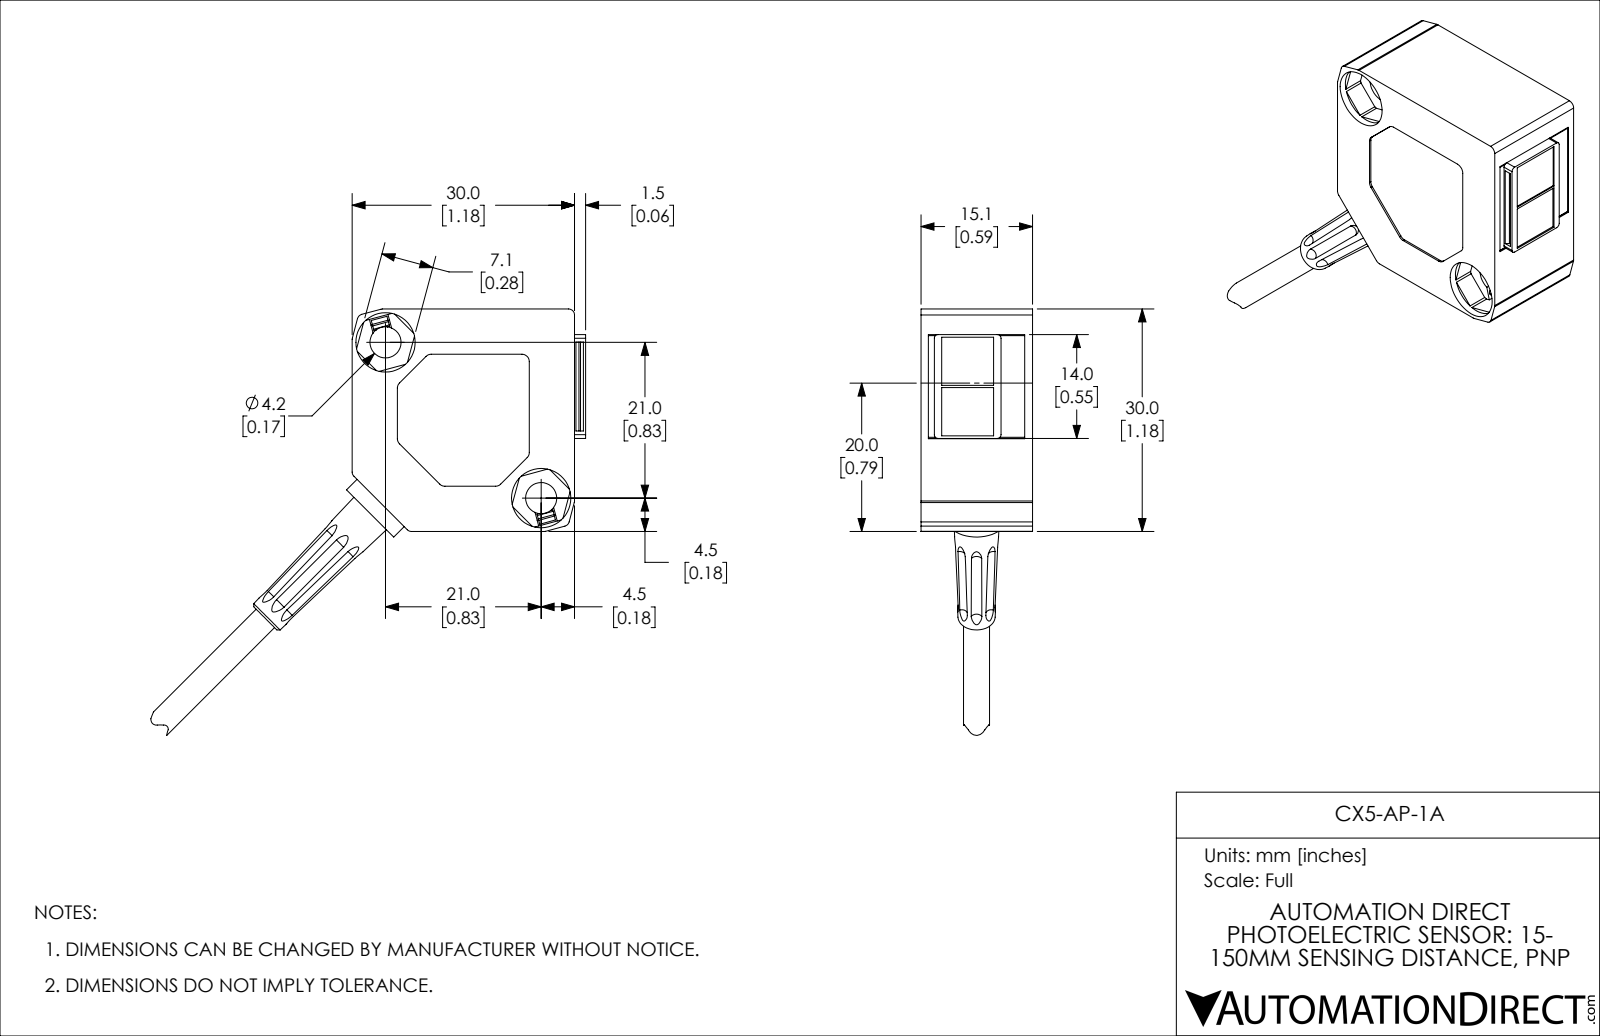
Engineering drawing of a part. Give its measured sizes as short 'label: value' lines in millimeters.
name: LHK_3031_303
written by: SolidWorks 2021 (AUTOMOTIVE_DESIGN)
unit: mm
bodies: 1 solid, 198 faces (116 planar, 62 cylindrical, 20 other)
size: 62.07 × 57.5 × 14.85
volume: 13 174 mm³; area: 4 946 mm²
holes: 2× ⌀2.2, 2× ⌀4.2, 2× ⌀8, 1× ⌀1.85, 1× ⌀7.6
bosses: 1× ⌀3.5
rounds: 17× R0.8, 7× R1, 4× R0.2, 2× R0.15, 2× R0.3, 2× R0.46, 2× R4.5, 1× R0.56
face distances: 14.85, 30, 14.6, 3.8, 11.05, 7.1, 3.55, 0.92, 33.75, 4.9
hole spacings: 1.73, 4.4, 5, 5.47, 5.86, 5.96, 29.7
